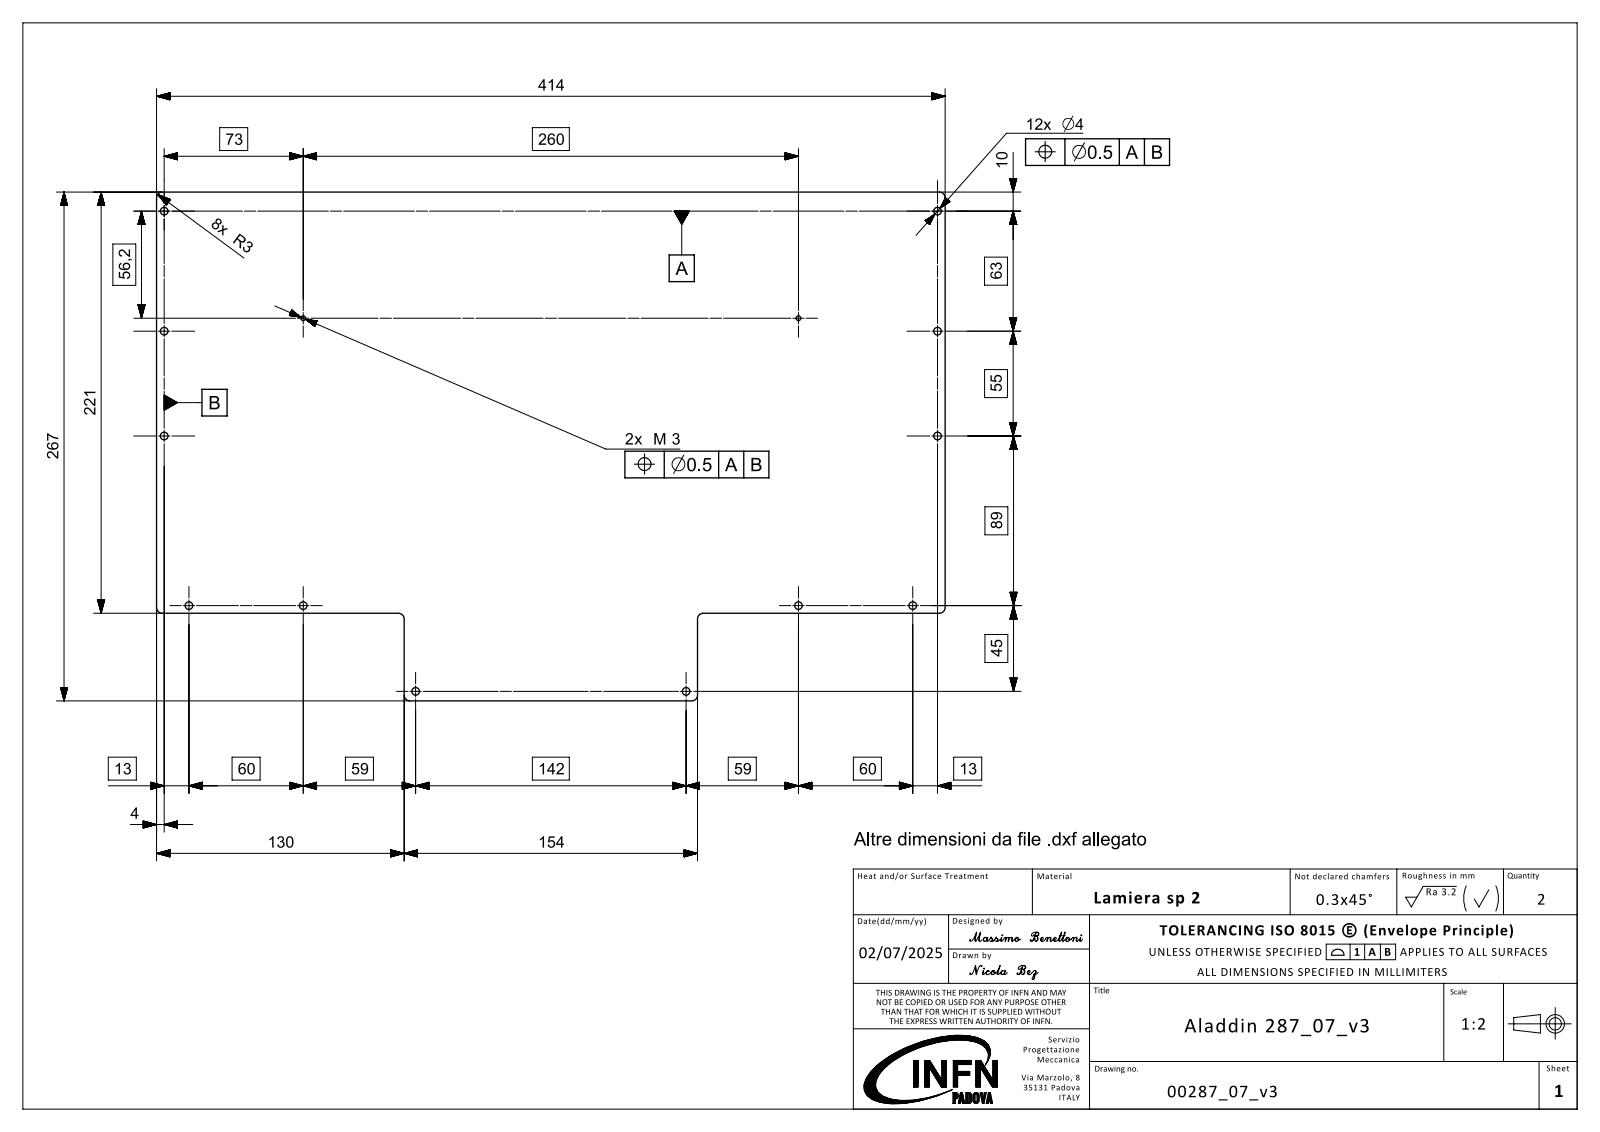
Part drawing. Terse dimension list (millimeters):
name: 00287_07_v3_objects
written by: SIEMENS PLM Software NX2306.9102 (AUTOMOTIVE_DESIGN)
unit: mm
bodies: 1 solid, 36 faces (10 planar, 22 cylindrical, 4 other)
size: 414 × 267 × 2
volume: 196 818 mm³; area: 199 851 mm²
holes: 12× ⌀4, 2× ⌀2.5
rounds: 8× R3
face distances: 2, 221, 414, 46, 267, 130, 284, 154
hole spacings: 406, 55, 60, 63, 73.32, 74.2, 89.94, 92.13
